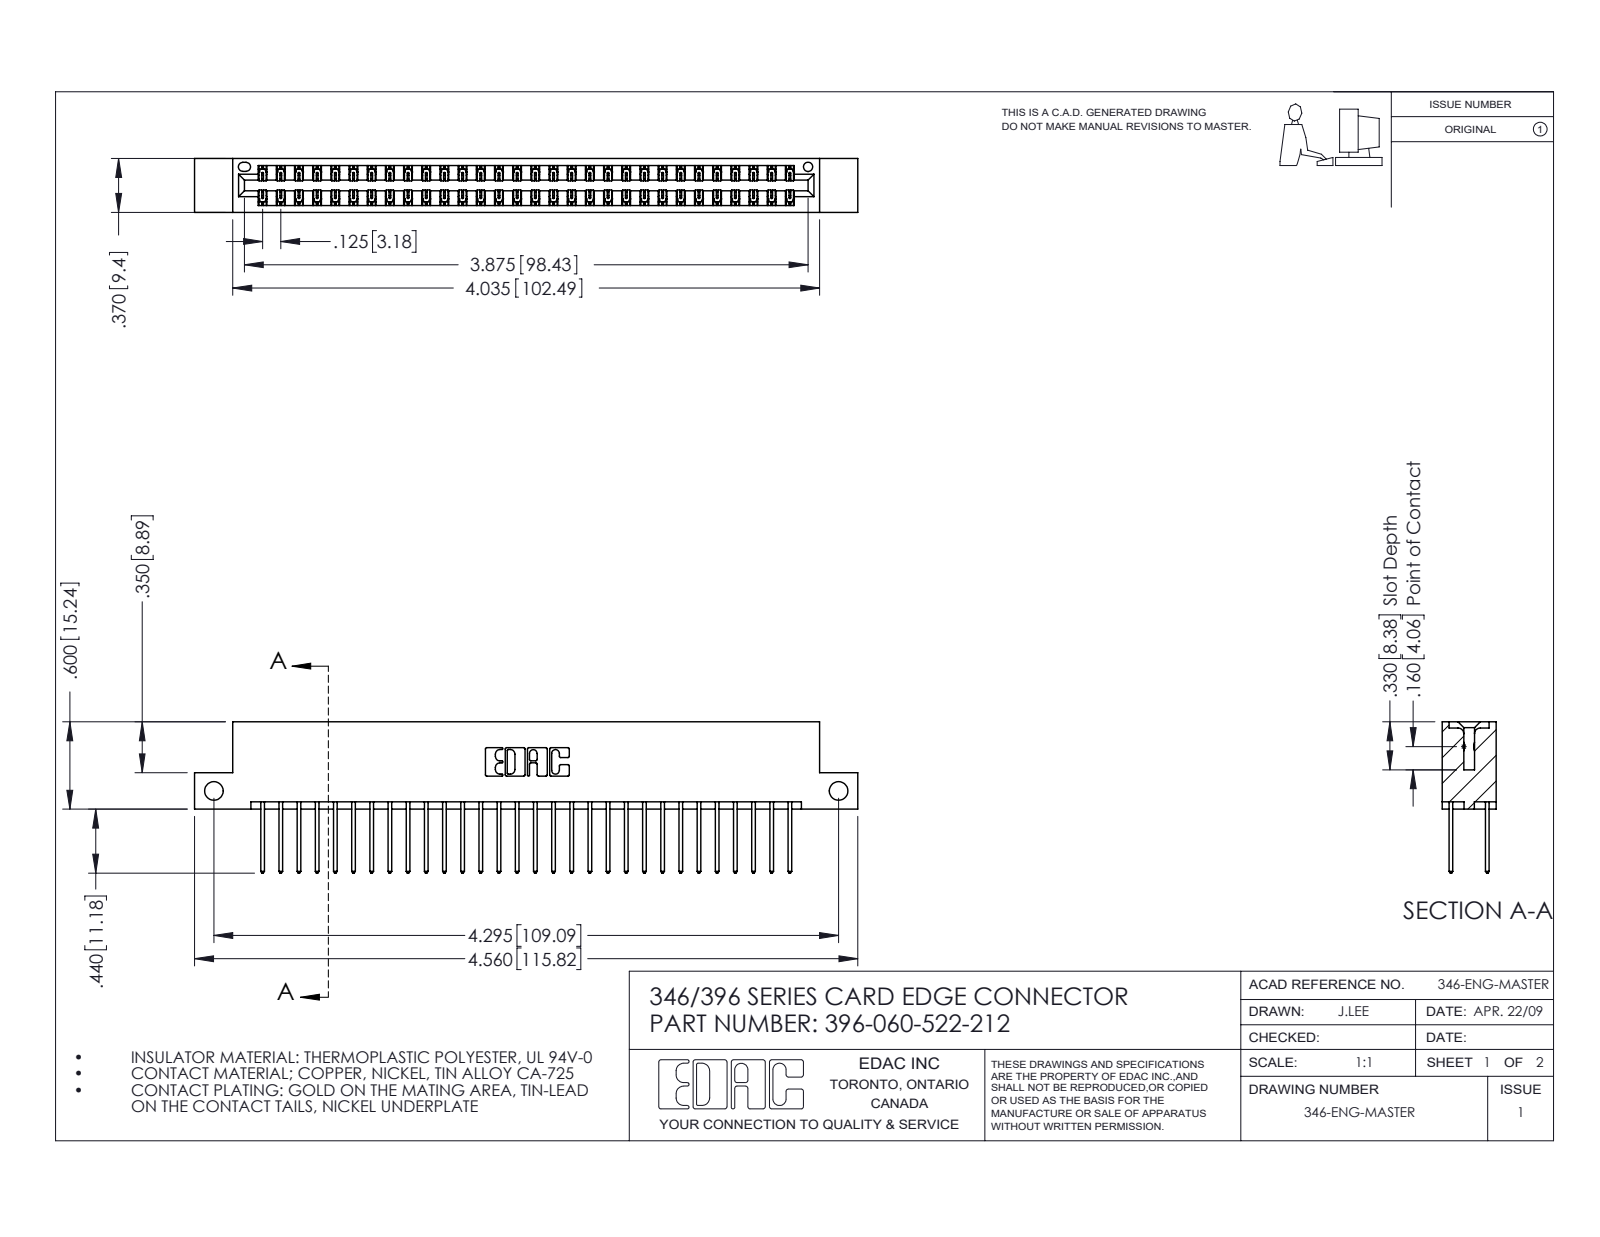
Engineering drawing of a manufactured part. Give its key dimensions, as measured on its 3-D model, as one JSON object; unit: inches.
{"part_name": "396-060-522-212; 345-292-001_345-293-122; 346 Part_Flush Mounting Lugs - Side Mount", "step_written_by": "SolidWorks 2016 (CONFIG_CONTROL_DESIGN)", "units": "inches", "bodies": {"solids": 61, "faces": 3242, "planar": 2176, "cylindrical": 1066, "other": 0}, "overall_size": [4.56, 1.04, 0.37], "volume_in3": 0.688, "surface_area_in2": 24.61, "round_holes": [[0.128, 2], [0.064, 1]], "partial_cylinders_radius": [[0.006, 90], [0.01, 60], [0.01, 22], [0.007, 6], [0.031, 6], [0.026, 3], [0.014, 2], [0.022, 2]], "face_to_face_distances": [0.048, 0.322, 0.25, 0.37, 0.072, 0.298, 0.025, 0.275, 0.148, 0.222], "hole_center_spacings": [4.295]}
